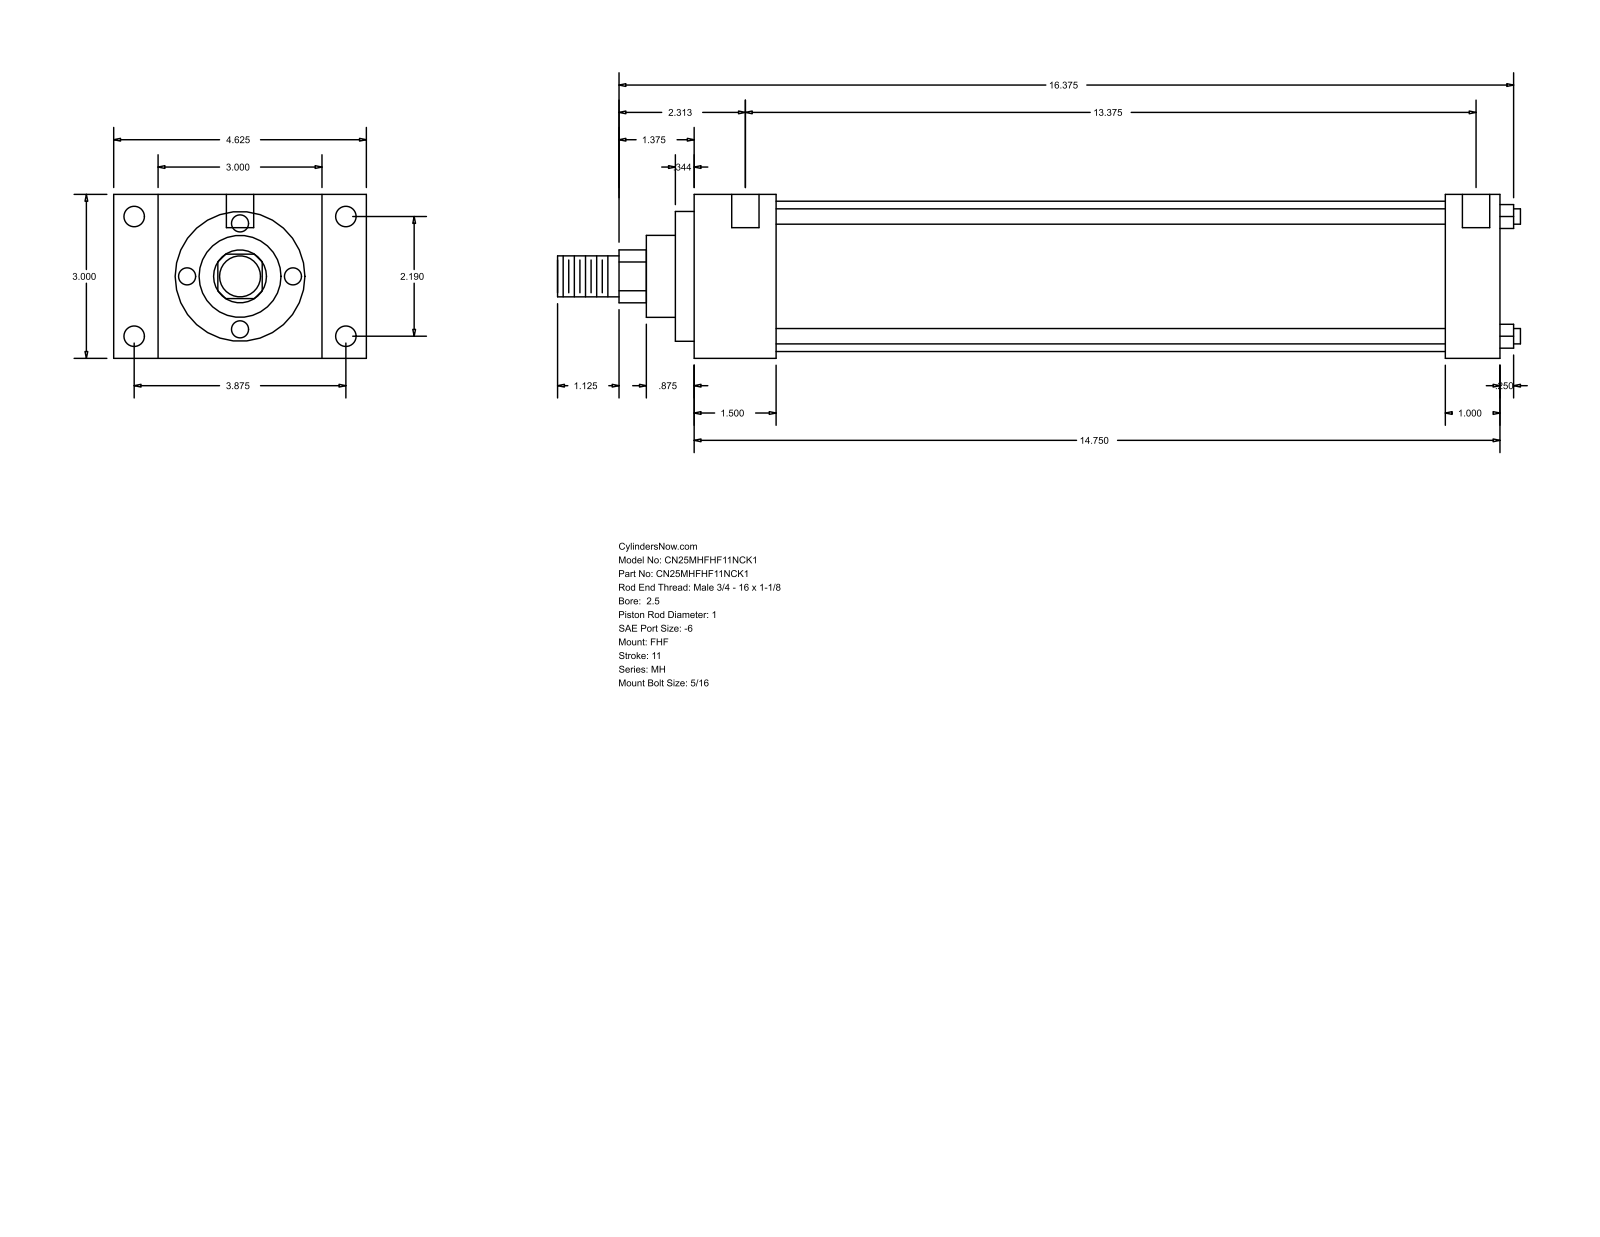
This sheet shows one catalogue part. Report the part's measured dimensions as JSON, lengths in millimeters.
{"part_name": "MH_FHF__0250_1", "step_written_by": "GSSL Pune (CONFIG_CONTROL_DESIGN)", "units": "millimeters", "bodies": {"solids": 0, "faces": 90, "planar": 61, "cylindrical": 29, "other": 0}, "overall_size": [447.68, 117.47, 76.2], "round_holes": [[5.56, 4], [9.53, 4], [12.7, 2]], "round_bosses_or_shafts": [[7.14, 4], [69.85, 1], [60.33, 1], [38.1, 1], [25.4, 1], [19.05, 1]], "partial_cylinders_radius": [[12.29, 1]], "face_to_face_distances": [76.2, 374.65, 38.11, 336.54, 20.64, 96.84, 117.48, 25.39, 349.26, 311.15], "hole_center_spacings": [55.62, 98.42, 113.05, 347.66, 3.18, 4.76, 339.72, 342.9]}
